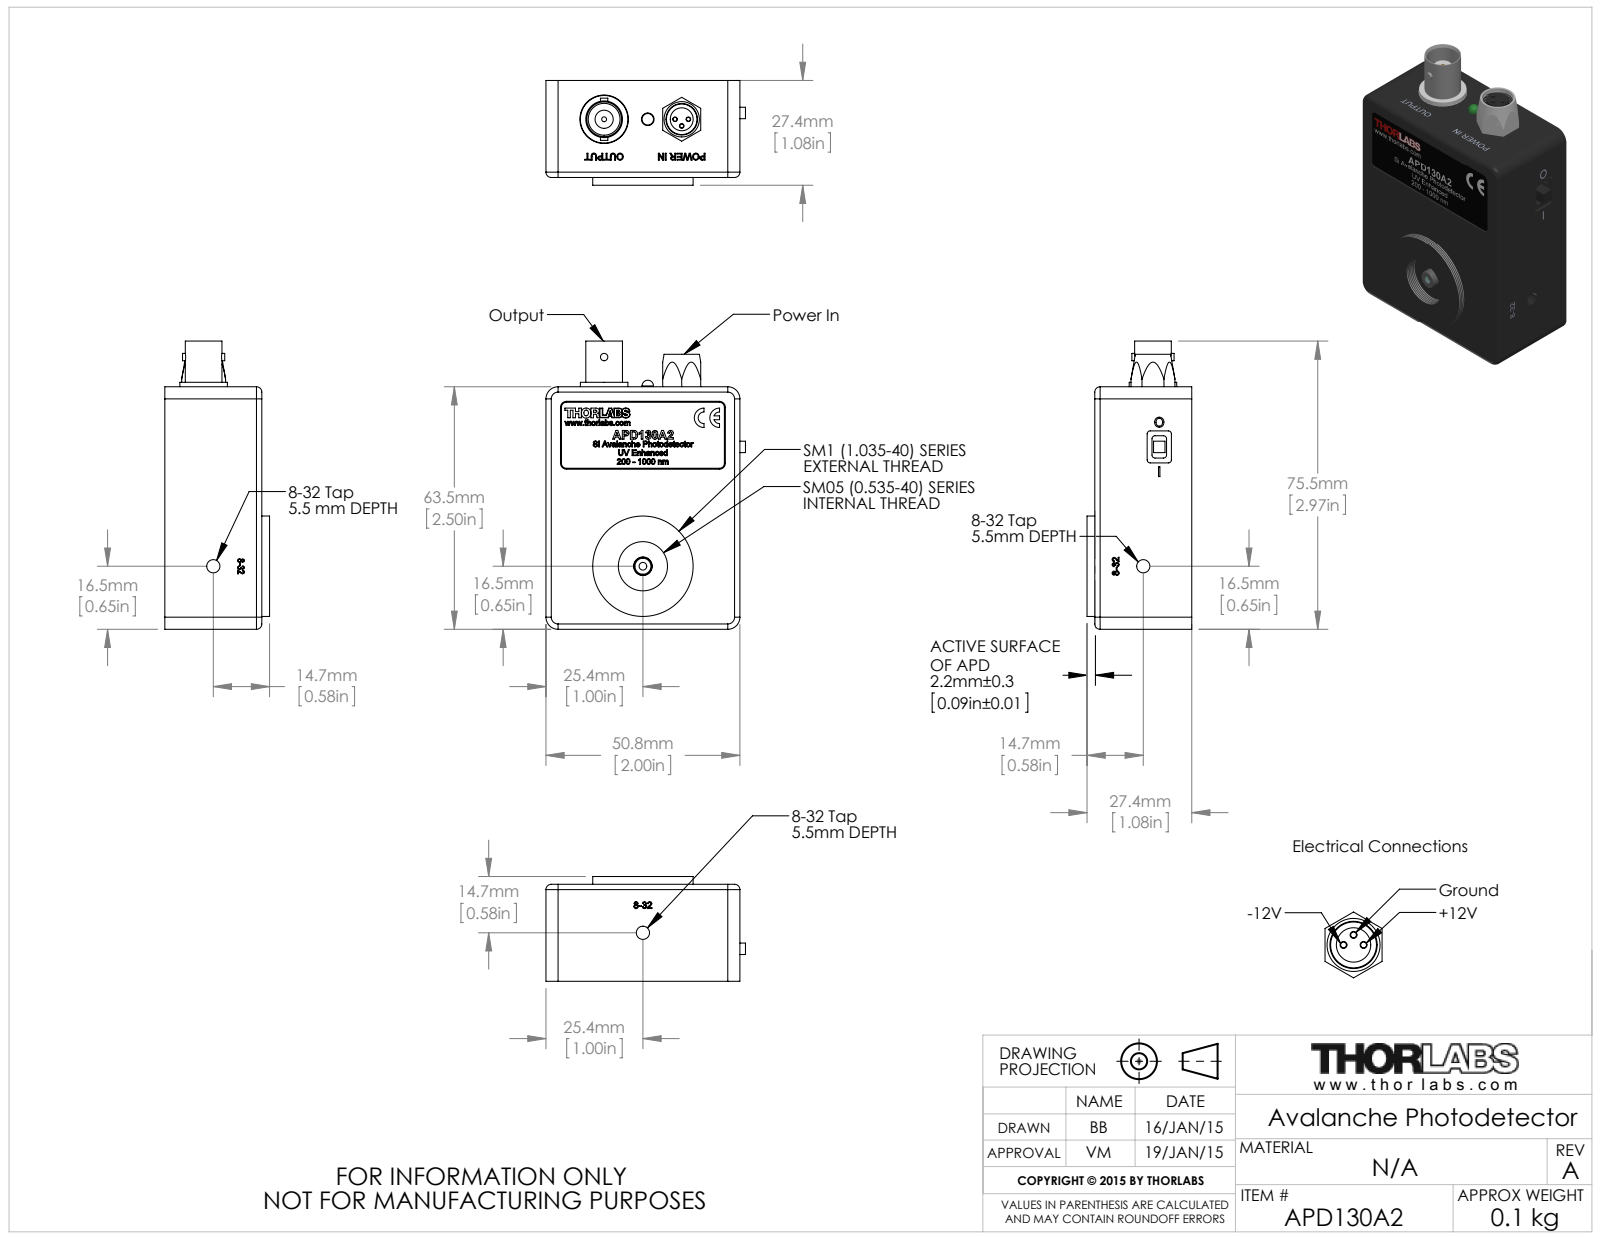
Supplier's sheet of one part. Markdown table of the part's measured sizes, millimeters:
| quantity | value |
| --- | --- |
| part name | MTN004761-E0W |
| STEP written by | SolidWorks 2014 (AUTOMOTIVE_DESIGN) |
| units | millimeters |
| bodies | 65 solids, 2135 faces (1071 planar, 252 cylindrical, 812 other) |
| overall size | 75.46 × 52.26 × 27.43 |
| volume | 36 135 mm³ |
| surface area | 28 949 mm² |
| round holes (diameter × count) | 1.6 × 8, 2.4 × 4, 1 × 3, 1.02 × 3, 3.45 × 2, 1.27 × 1, 1.32 × 1, 2 × 1, 2.5 × 1, 3.3 × 1, 4.14 × 1, 4.85 × 1 |
| round bosses / shafts (diameter × count) | 0.51 × 6, 3.8 × 5, 2 × 4, 0.45 × 3, 26.29 × 1, 12.45 × 1, 10.92 × 1, 9.6 × 1 |
| partial cylindrical surfaces (radius × count) | 3.17 × 18, 3.3 × 14, 0.79 × 8, 1.91 × 8, 2.41 × 8, 2.54 × 5, 1.27 × 4, 1.4 × 4 |
| main face-to-face distances | 1.59, 2.54, 25.4, 23.81, 1.14, 0.51, 24.89, 23.3, 1.65, 23.75 |
| hole center spacings | 4.41, 41.17, 51.14, 65.51, 1.27, 1.75, 1.8, 2.47 |
